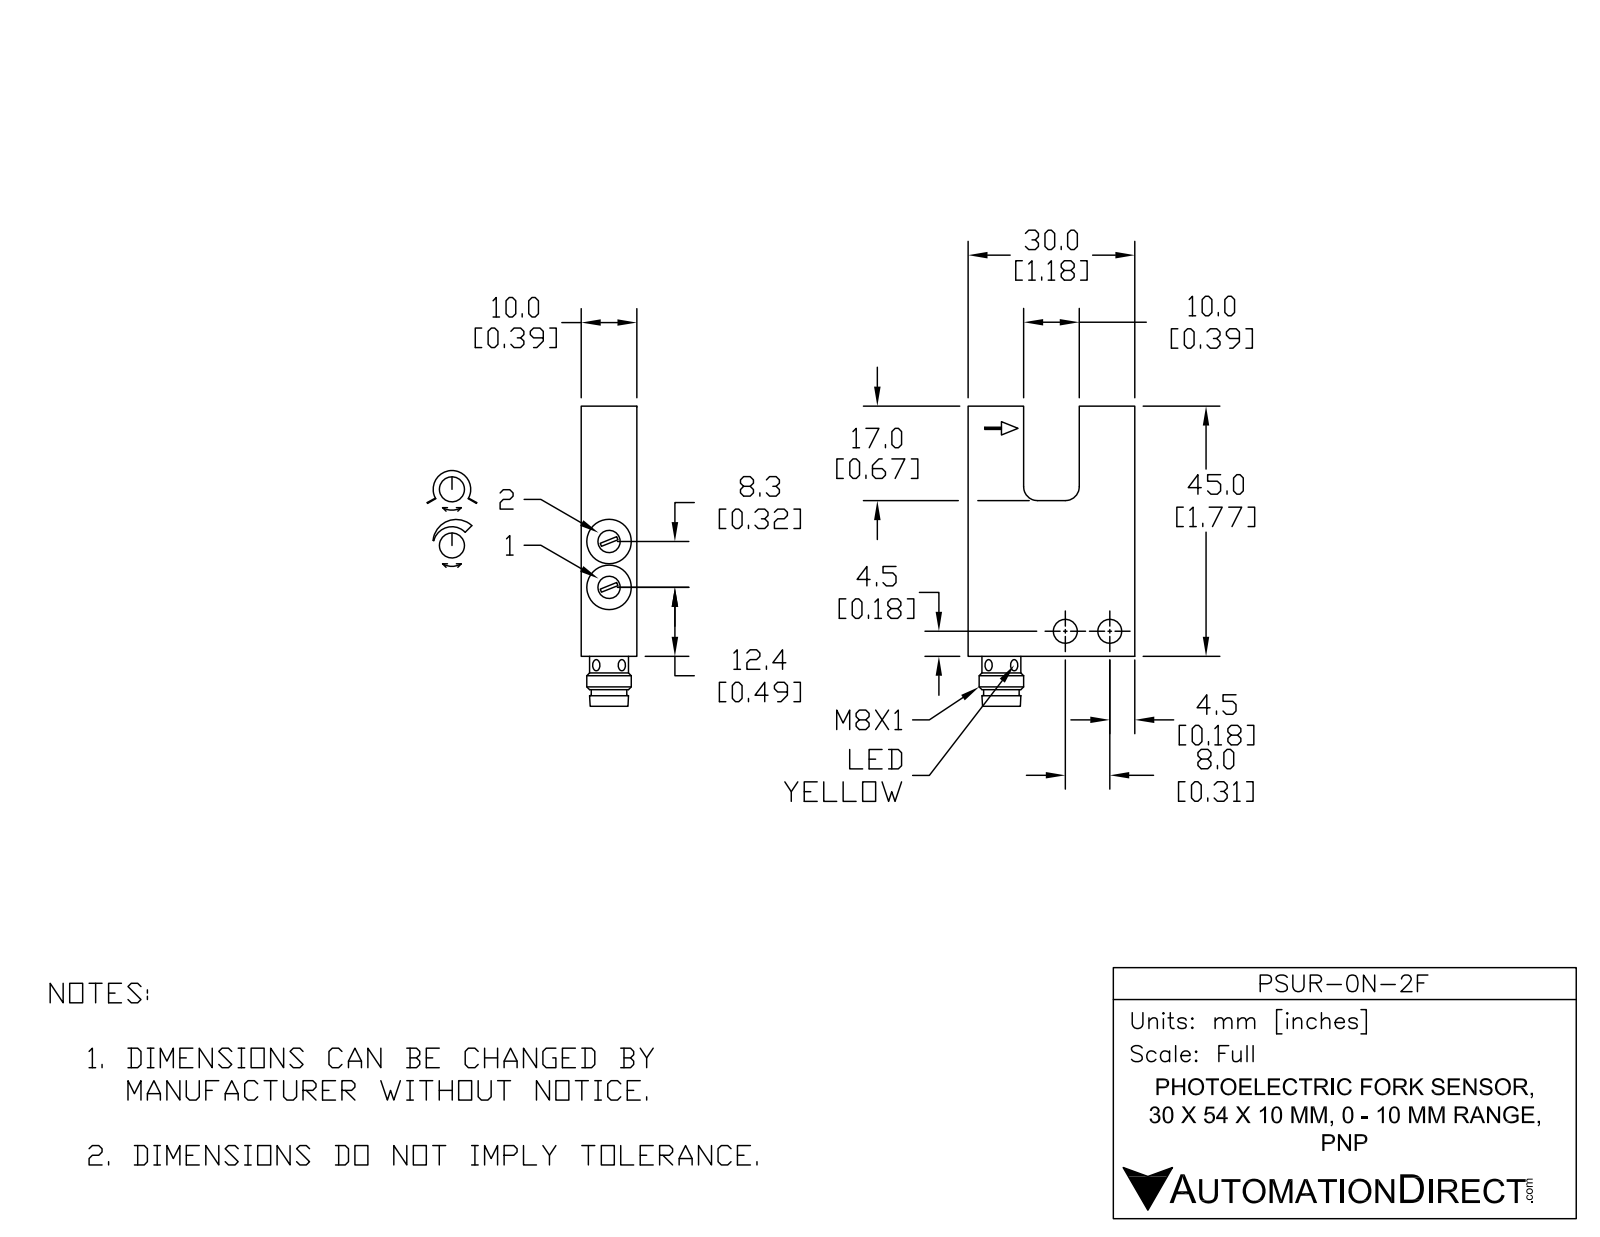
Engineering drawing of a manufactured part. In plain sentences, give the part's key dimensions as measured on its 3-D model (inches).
The part is named "PSUR-0N-2F". Its 3-D file was written by "SolidWorks 2016 (AUTOMOTIVE_DESIGN)". It is 1 solid with 75 faces: 35 planar, 34 cylindrical and 6 other. Overall it measures 2.126 by 1.181 by 0.394 inches. Its volume is 0.716 cubic inches and its surface area 7.329 square inches. Round holes: 2 of diameter 0.079, 2 of diameter 0.157, 2 of diameter 0.169, 2 of diameter 0.315, 1 of diameter 0.228. Round bosses or shafts: 1 of diameter 0.315, 1 of diameter 0.267. Partial cylindrical surfaces (rounded edges, fillets, slot ends): 2 of radius 0.063, 2 of radius 0.098. The main face-to-face distances are 0.394, 1.181, 0.787, 1.772, 0.39, 1.177, 0.783, 0.669, 1.102, 0.157. The hole center spacings are 0.315, 0.325.
